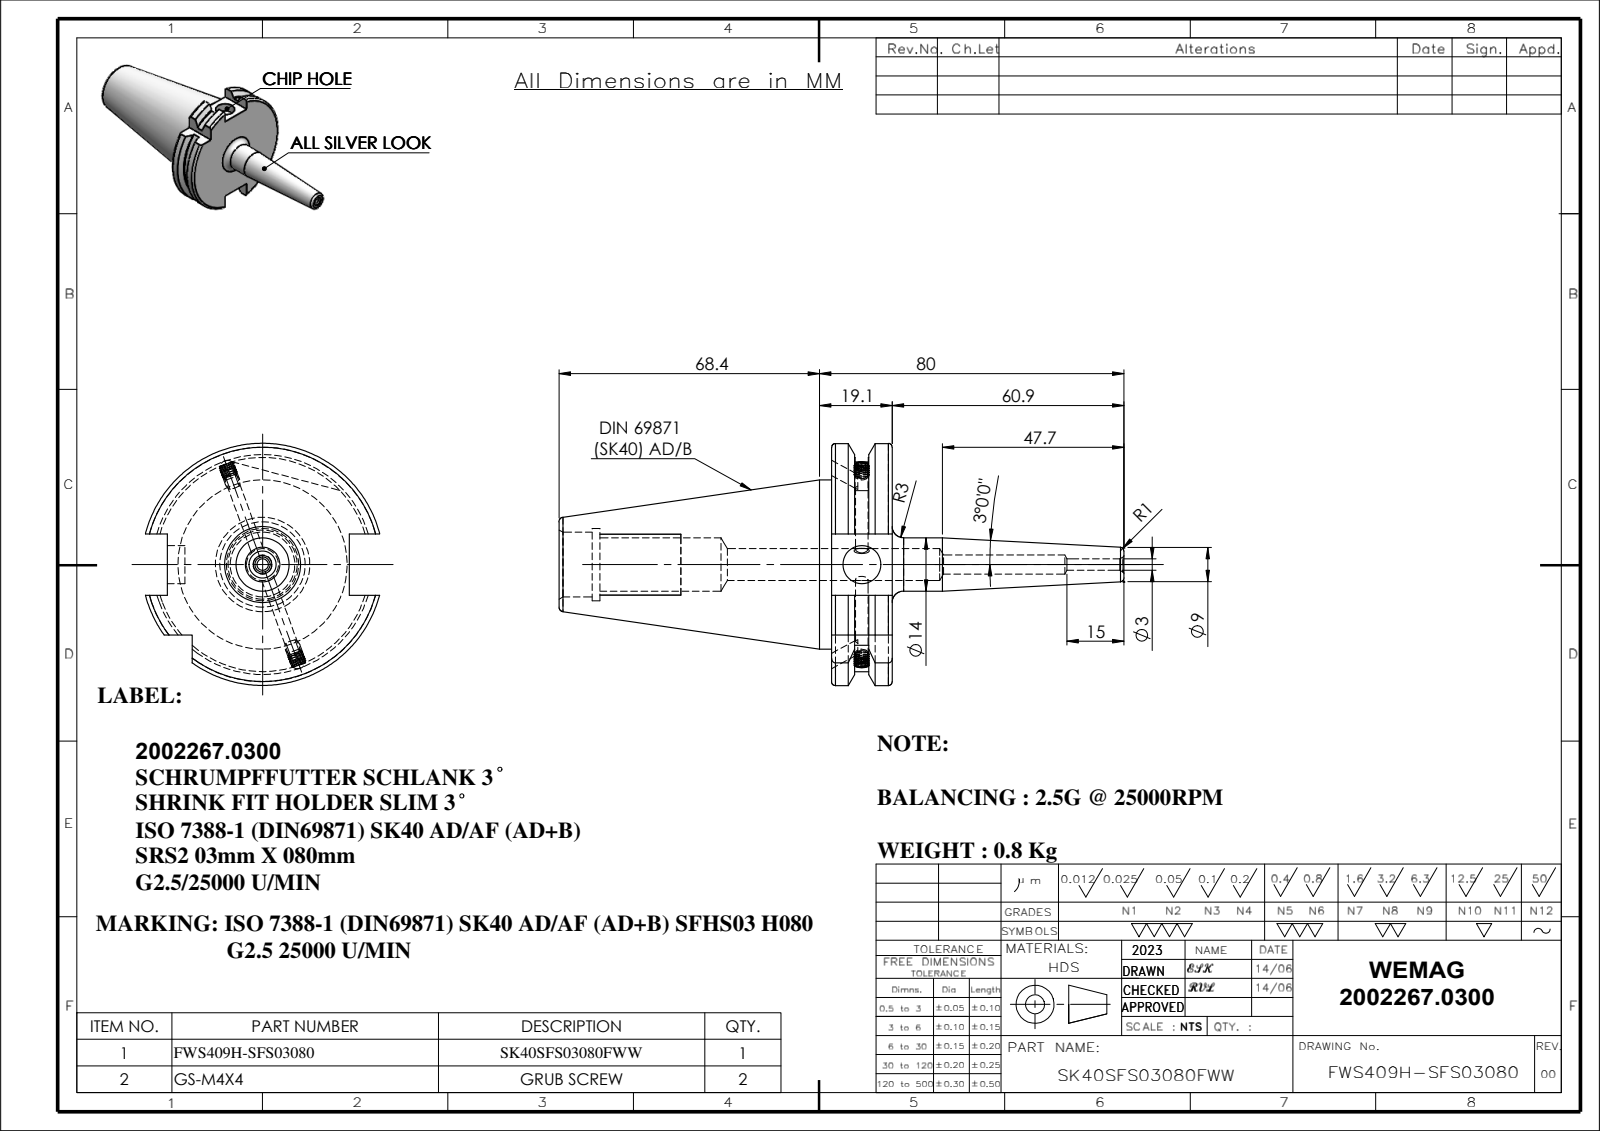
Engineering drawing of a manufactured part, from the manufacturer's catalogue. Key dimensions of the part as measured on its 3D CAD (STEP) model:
Part name (STEP PRODUCT): GS-M4X4_DIN 913 - M4 x 4-N; SK40SFS03080FWW; 91406-SRS203080
STEP written by: SolidWorks 2018 (CONFIG_CONTROL_DESIGN)
Units: millimetres
Bodies: 3 solids, 198 faces (46 planar, 54 cylindrical, 98 other)
Overall size (bounding box): 148.4 × 63.55 × 61.48
Volume: 108 361 mm³ · Surface area: 24 117 mm²
Round holes (diameter × count): ⌀3 ×1, ⌀3.3 ×1, ⌀5 ×1, ⌀8.4 ×1, ⌀10 ×1, ⌀14 ×1, ⌀17 ×1, ⌀19 ×1
Round bosses / shafts (diameter × count): ⌀4 ×2, ⌀44.45 ×1
Partial cylindrical surfaces — rounded edges, fillets, slot ends (radius × count): R28.12 ×1, R31.77 ×1
Main face-to-face distances: 15.9, 16.1, 47.8, 60.9, 76.8, 71.6, 87.5, 10.7, 77.63, 66.93
